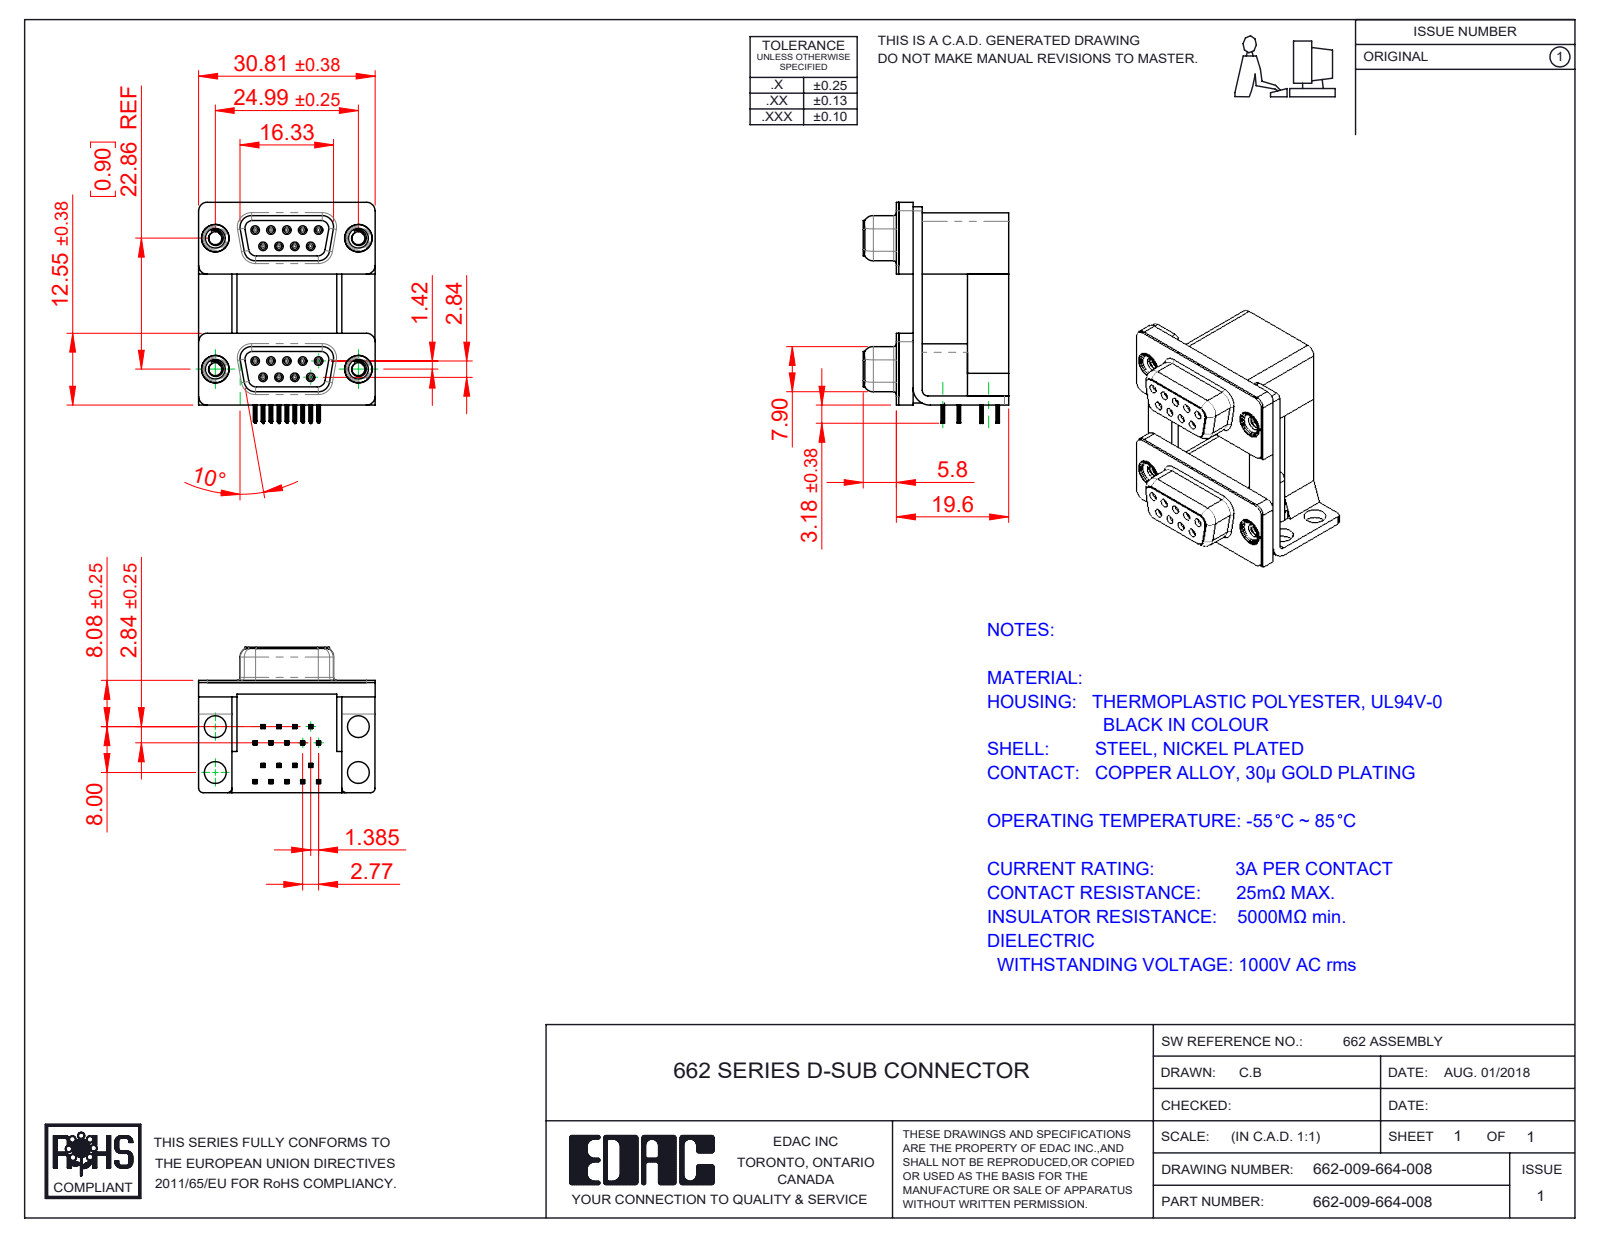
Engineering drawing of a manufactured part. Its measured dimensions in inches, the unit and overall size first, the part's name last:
Units: inches
Overall size (bounding box): 1.519 × 1.213 × 1
Round holes (diameter × count): ⌀0.031 ×18, ⌀0.035 ×18, ⌀0.089 ×4, ⌀0.138 ×4, ⌀0.15 ×4, ⌀0.157 ×4, ⌀0.189 ×4, ⌀0.197 ×4
Round bosses / shafts (diameter × count): ⌀0.047 ×18, ⌀0.193 ×4, ⌀0.187 ×4, ⌀0.154 ×4
Partial cylindrical surfaces — rounded edges, fillets, slot ends (radius × count): R0.004 ×144, R0.006 ×72, R0.014 ×36, R0.013 ×18, R0.053 ×16, R0.059 ×13, R0.011 ×8, R0.02 ×8
Main face-to-face distances: 0.098, 0.657, 0.756, 0.016, 0.9, 0.374, 0.283, 0.472, 0.114, 0.063
Hole centre spacings: 0.124, 0.109, 0.907, 0.9, 0.218, 0.926, 0.79, 1.013
Volume: 0.721 in³ · Surface area: 21.2 in²
Bodies: 29 solids, 3110 faces (1374 planar, 796 cylindrical, 940 other)
Part name (STEP PRODUCT): 662-009-664-008; 662 Housing Upper_09 Contacts H; 662 Housing Lower_09 Contacts; 662 Contact Bottom Lower (+7 more)
STEP written by: SolidWorks 2020 (CONFIG_CONTROL_DESIGN)
